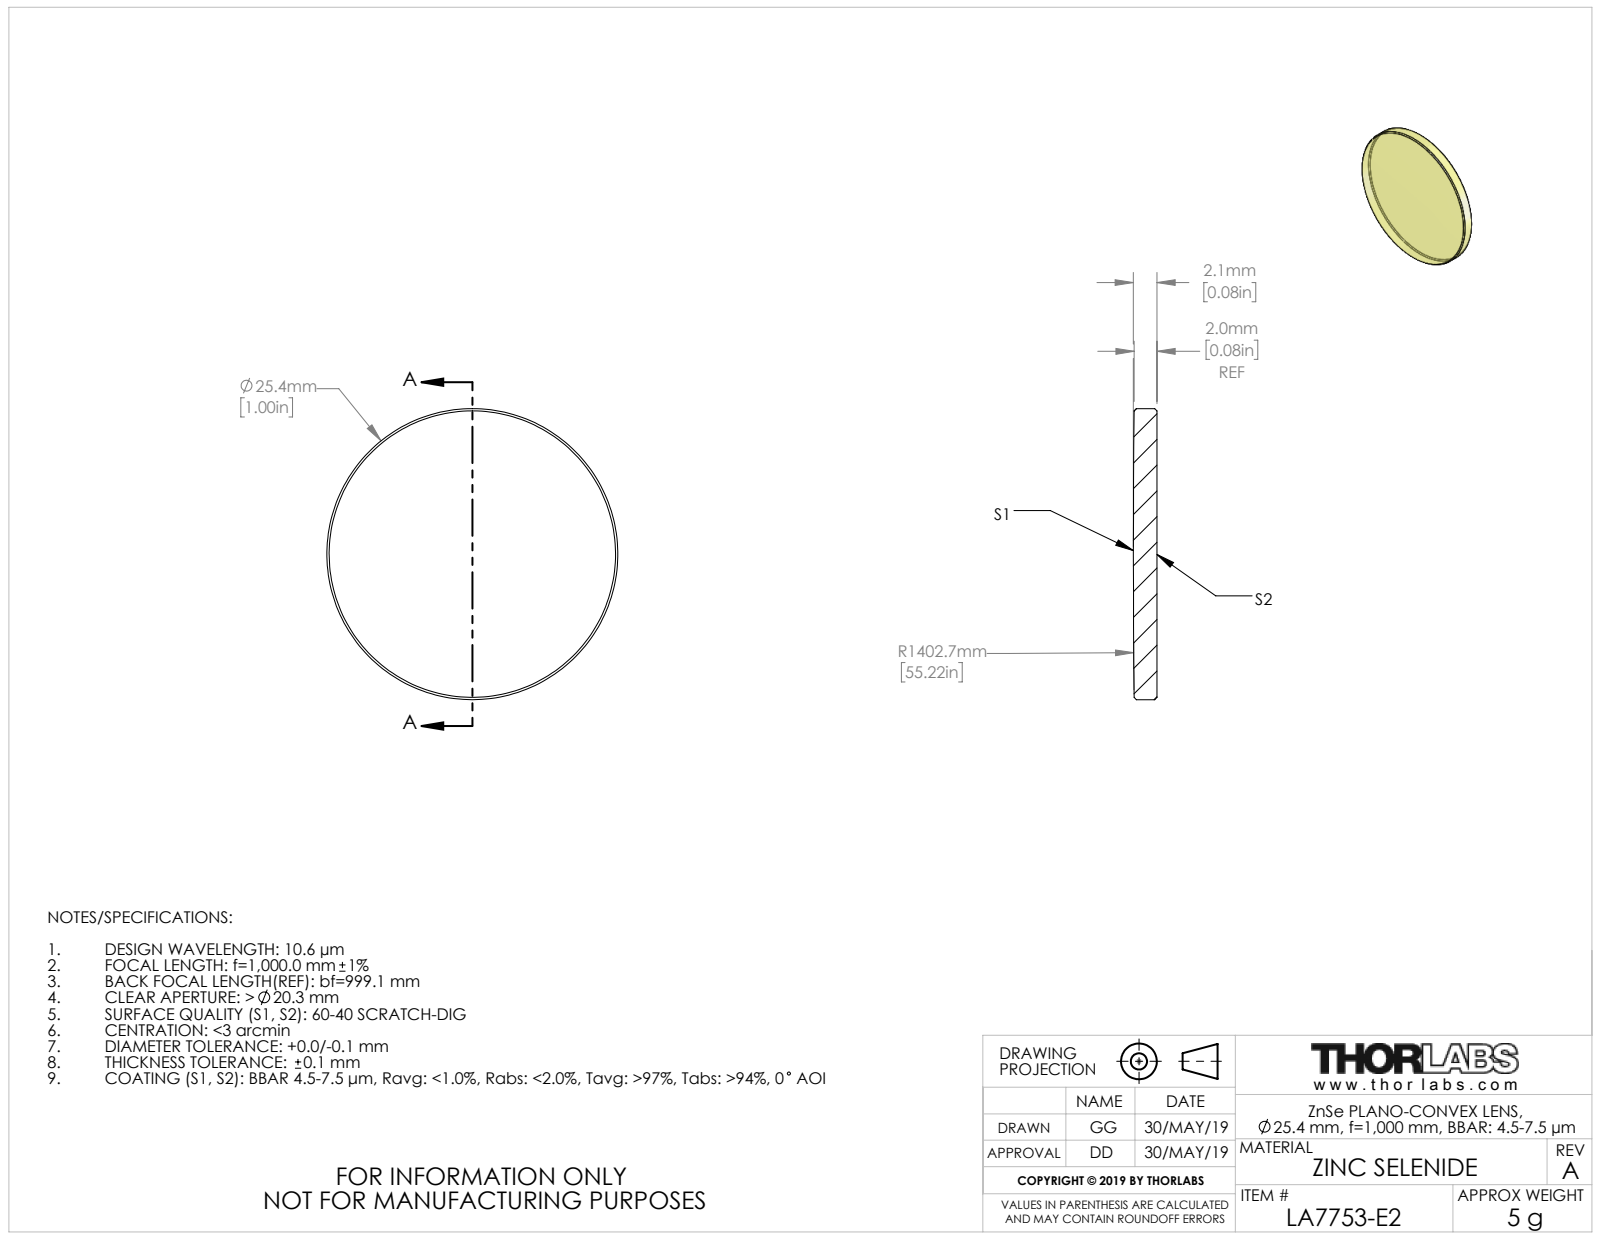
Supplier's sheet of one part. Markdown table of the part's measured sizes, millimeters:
| quantity | value |
| --- | --- |
| part name | TTN047620-E0W |
| STEP written by | SolidWorks 2018 (CONFIG_CONTROL_DESIGN) |
| units | millimeters |
| bodies | 1 solid, 9 faces (1 planar, 2 cylindrical, 6 other) |
| overall size | 25.4 × 25.4 × 2.06 |
| volume | 1 026 mm³ |
| surface area | 1 155 mm² |
| round bosses / shafts (diameter × count) | 25.4 × 1 |
